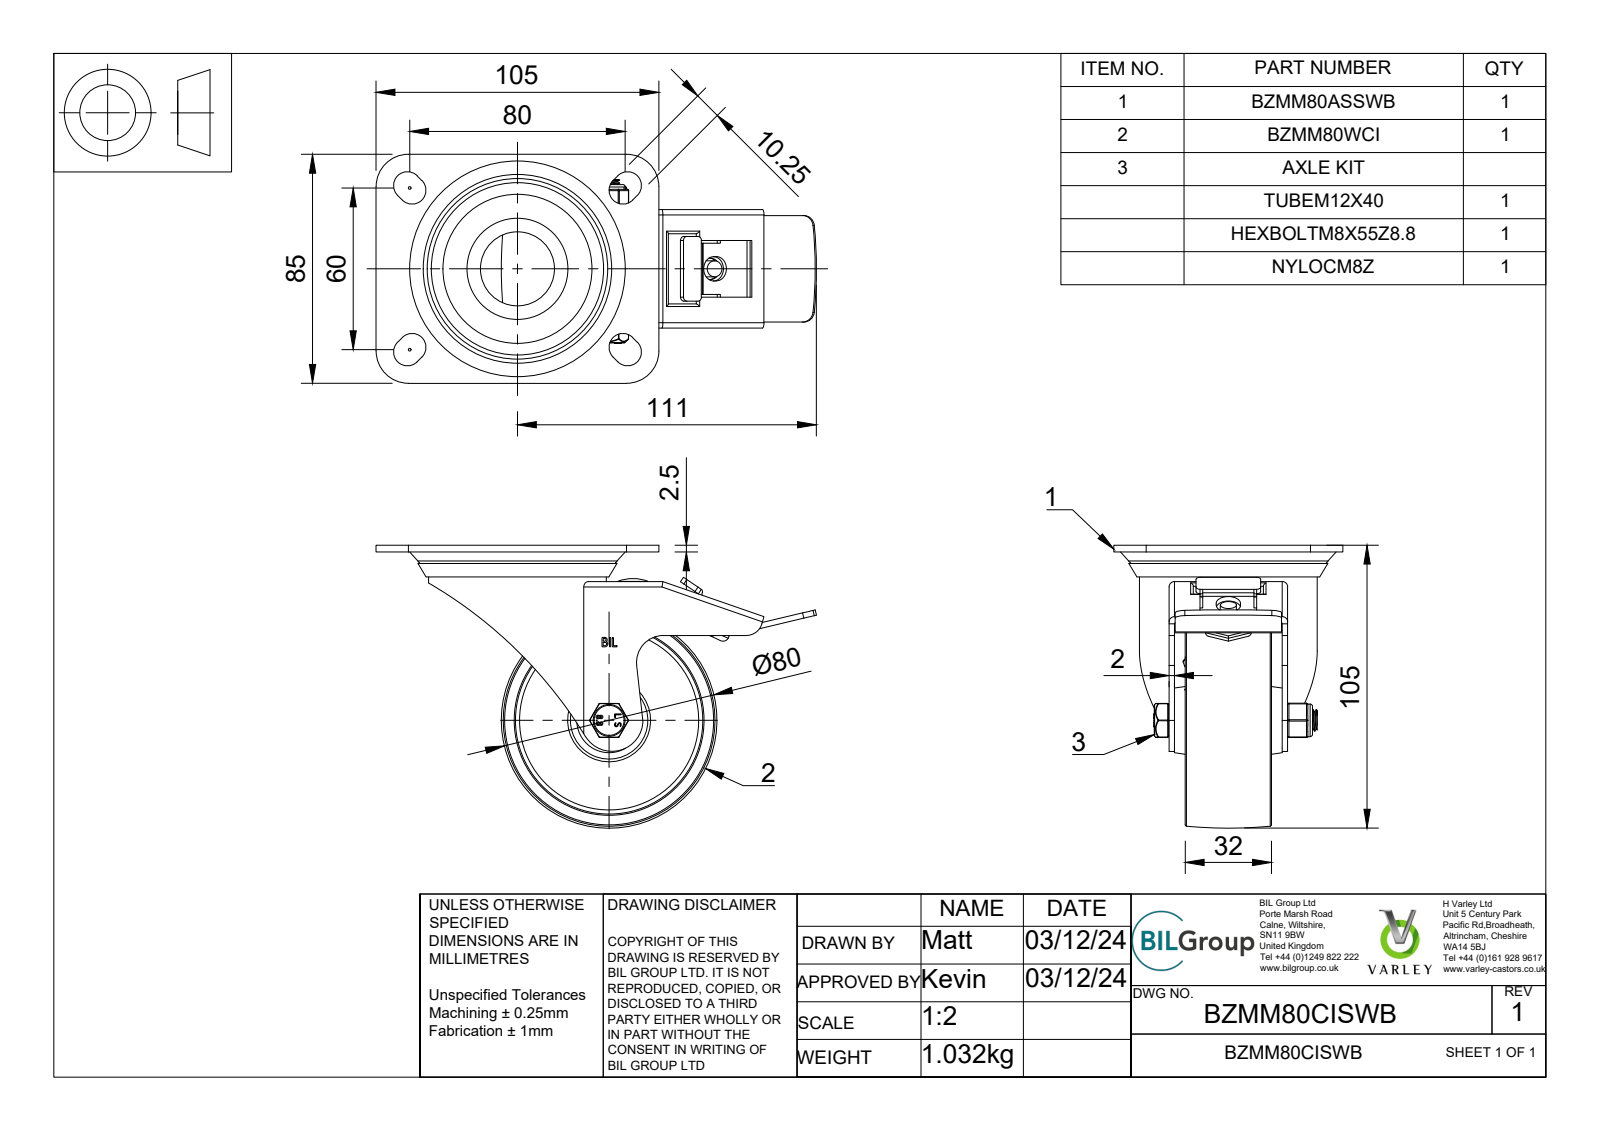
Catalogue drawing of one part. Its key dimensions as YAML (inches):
part_name: "BZMM80CISWB v3; BZMM80ASSWB v1; ZINC PLATED, PRESSED STEEL TOP PLATE; ZINC PLATED, PRESSED STEEL TOP PLATE Geometry (+7 more)"
step_written_by: "Autodesk Translation Framework v13.20.0.188 (AP242_MANAGED_MODEL_BASED_3D_ENGINEERING_MIM_LF)"
units: inches
bodies: {solids: 38, faces: 645, planar: 304, cylindrical: 202, other: 139}
overall_size: [6.437, 4.134, 3.346]
volume: 8.617
surface_area: 150.1
round_holes:
  - {diameter: 0.026, count: 2}
  - {diameter: 0.315, count: 2}
  - {diameter: 0.157, count: 1}
  - {diameter: 0.236, count: 1}
  - {diameter: 0.323, count: 1}
  - {diameter: 0.331, count: 1}
  - {diameter: 0.339, count: 1}
  - {diameter: 0.48, count: 1}
  - {diameter: 1.083, count: 1}
  - {diameter: 2.205, count: 1}
  - {diameter: 2.441, count: 1}
  - {diameter: 2.736, count: 1}
round_bosses_or_shafts:
  - {diameter: 2.598, count: 1}
  - {diameter: 1.24, count: 1}
  - {diameter: 0.476, count: 1}
  - {diameter: 0.469, count: 1}
  - {diameter: 0.453, count: 1}
  - {diameter: 0.31, count: 1}
  - {diameter: 0.254, count: 1}
  - {diameter: 0.236, count: 1}
partial_cylinders:
  - {radius: 0.01, count: 30}
  - {radius: 0.02, count: 24}
  - {radius: 0.039, count: 16}
  - {radius: 0.079, count: 11}
  - {radius: 0.202, count: 8}
  - {radius: 0.013, count: 4}
  - {radius: 0.025, count: 4}
  - {radius: 0.059, count: 4}
face_to_face_distances: [0.079, 0.098, 0.699, 0.876, 0.177, 0.778, 0.955, 1.654, 0.512, 0.039]
hole_center_spacings: [0.127, 0.098, 1.687]
